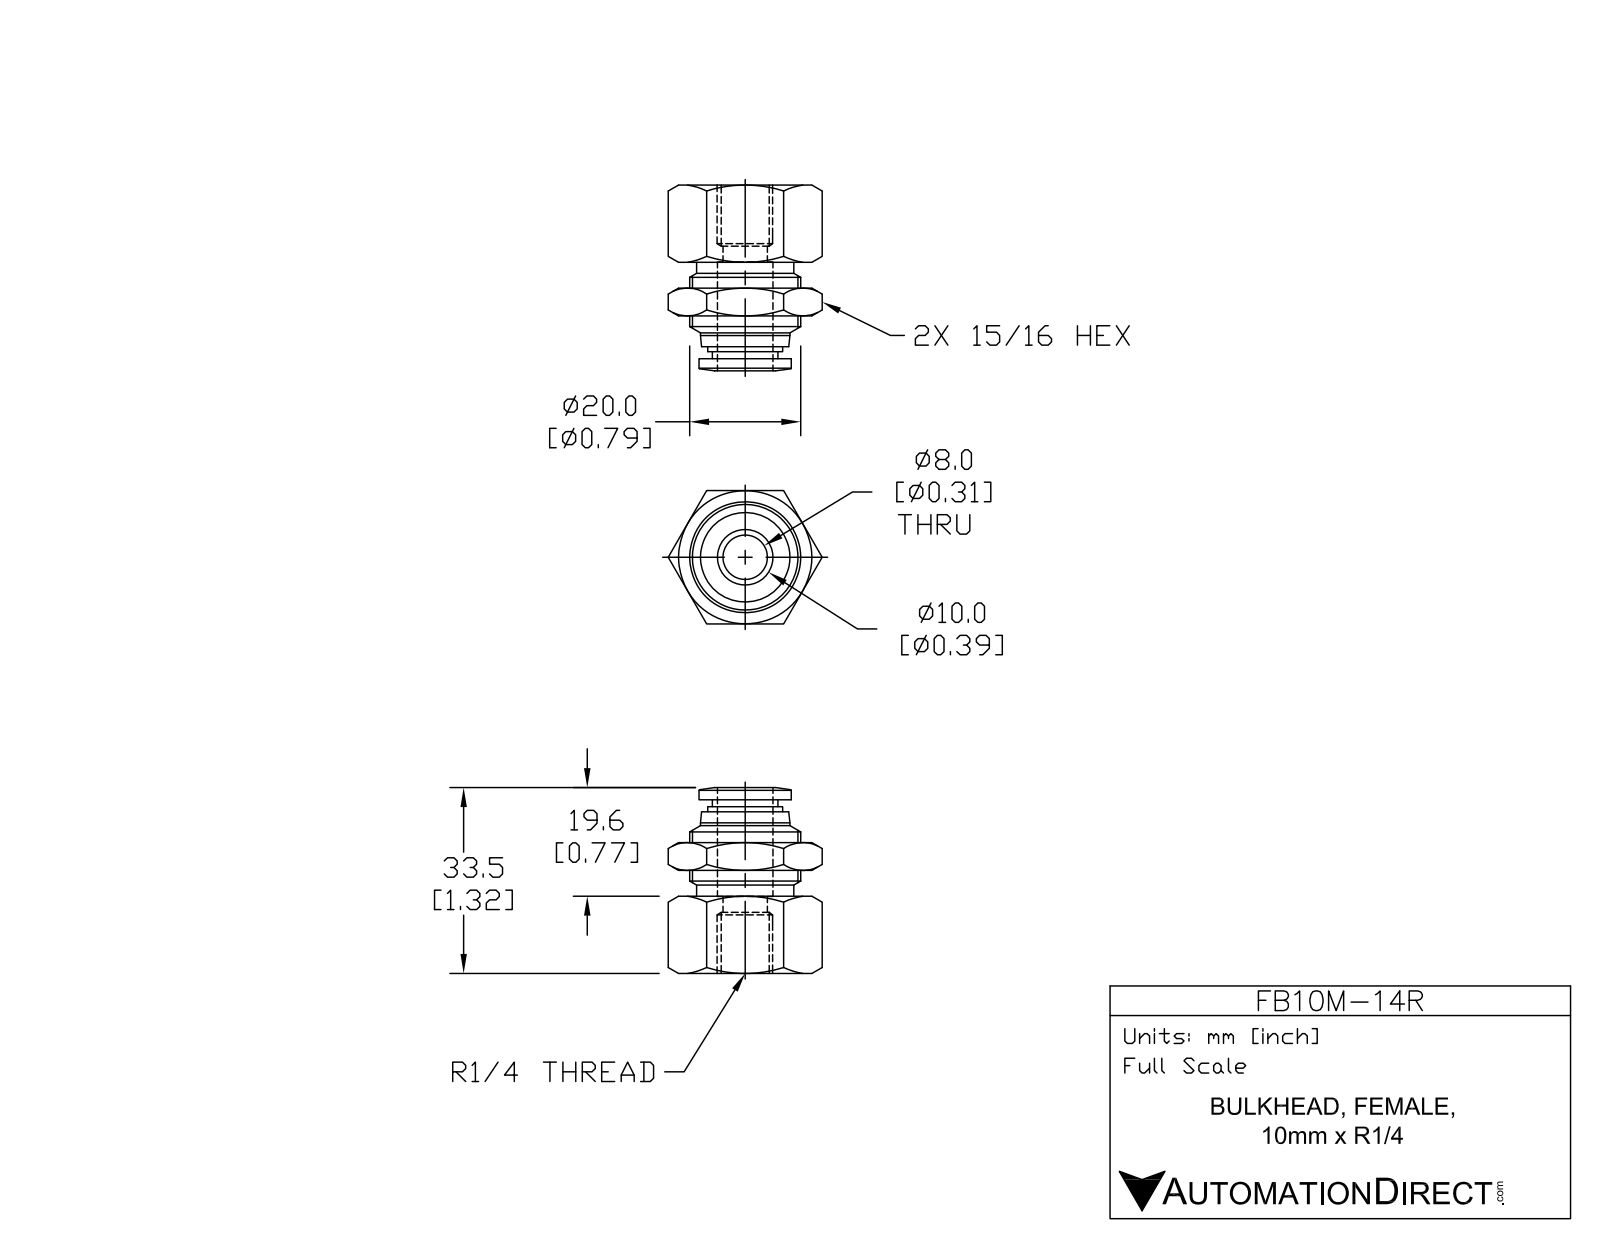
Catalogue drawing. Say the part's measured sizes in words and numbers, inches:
The part is named "FB10M-14R". Its 3-D file was written by "SolidWorks 2015 (AUTOMOTIVE_DESIGN)". It is 1 solid with 82 faces: 22 planar, 18 cylindrical and 42 other. Overall it measures 1.321 by 1.091 by 0.945 inches. Its volume is 0.587 cubic inches and its surface area 7.628 square inches. Round holes: 1 of diameter 0.315, 1 of diameter 0.406. Round bosses or shafts: 1 of diameter 0.787, 1 of diameter 0.689, 1 of diameter 0.654, 1 of diameter 0.634, 1 of diameter 0.531, 1 of diameter 0.465. The main face-to-face distances are 0.945, 0.551, 0.731, 0.18, 0.928, 0.376, 0.197, 1.234, 0.683, 0.504.
